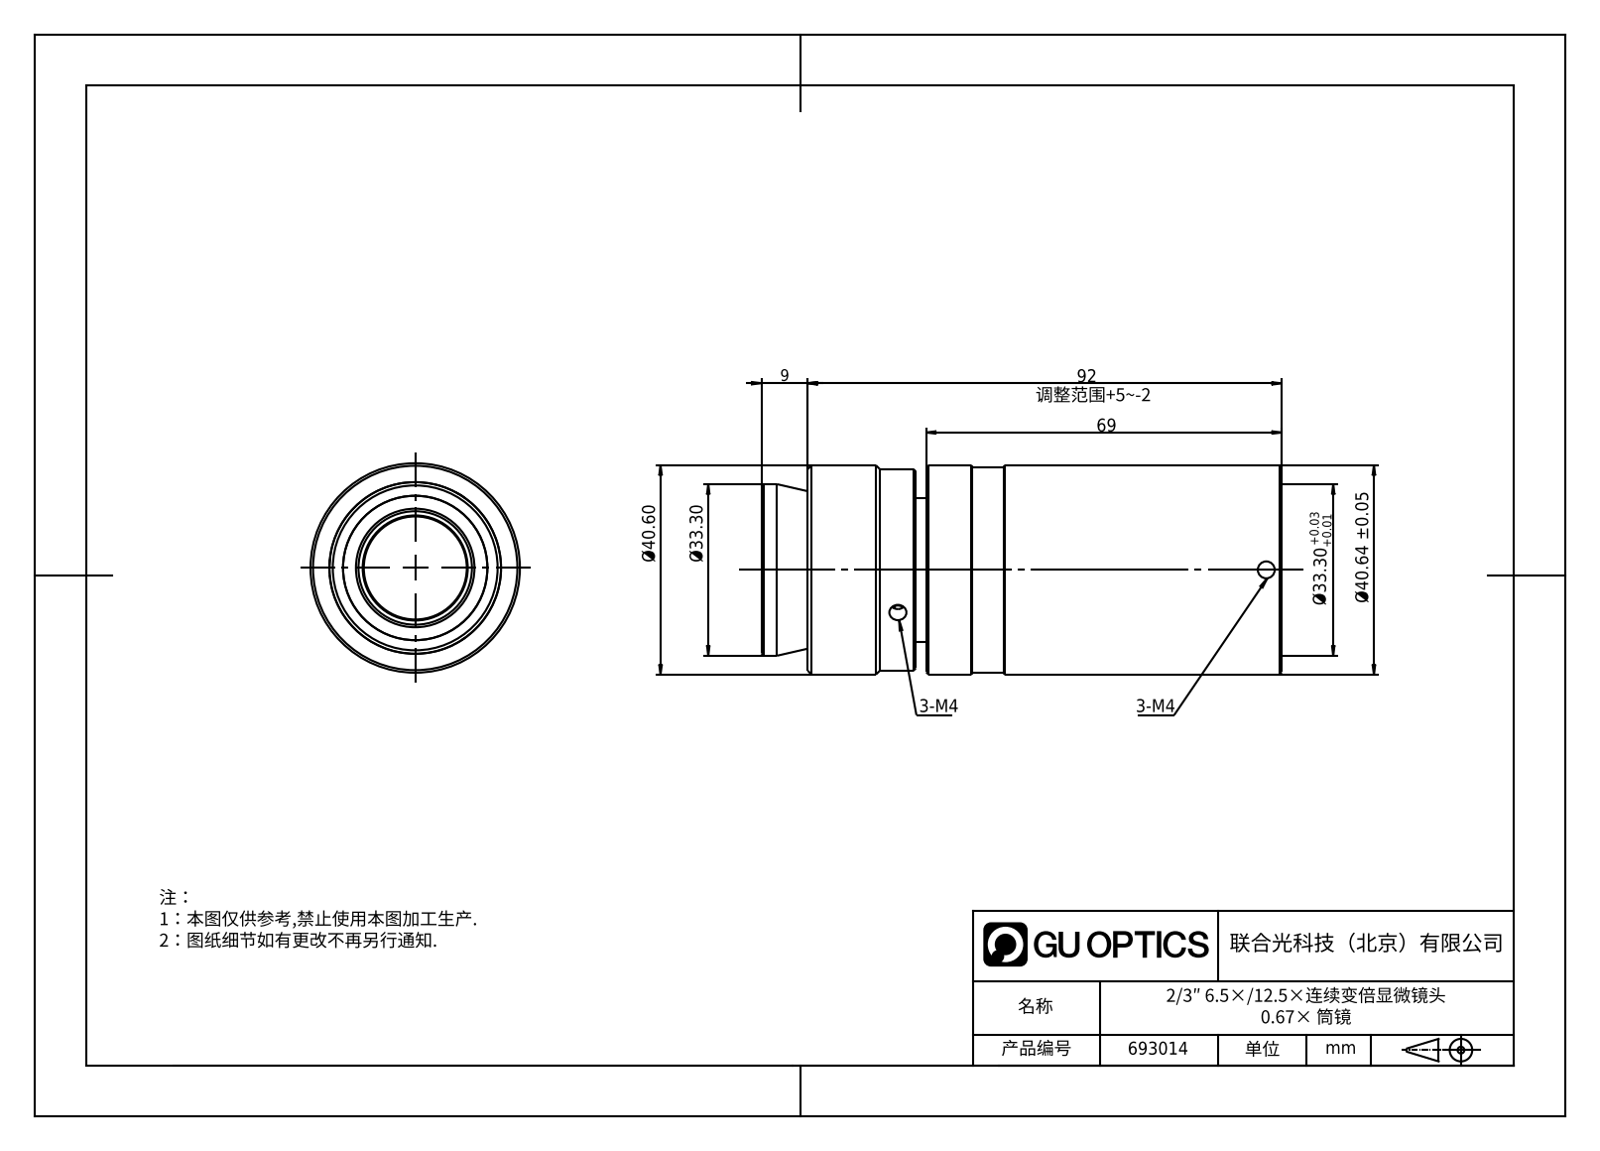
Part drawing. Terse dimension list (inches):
name: 693014
written by: SolidWorks 2020 (CONFIG_CONTROL_DESIGN)
unit: in
bodies: 2 solids, 47 faces (14 planar, 24 cylindrical, 9 other)
size: 3.976 × 1.6 × 1.6
volume: 3.632 in³; area: 45.63 in²
holes: 3× ⌀0.118, 3× ⌀0.13, 1× ⌀0.787, 1× ⌀0.906, 1× ⌀0.945, 1× ⌀1.081, 1× ⌀1.11, 1× ⌀1.181, 1× ⌀1.26, 1× ⌀1.311
bosses: 1× ⌀1.6, 1× ⌀1.575, 1× ⌀1.516, 1× ⌀1.102
face distances: 0.079, 0.709, 0.472, 0.906, 0.354, 2.795, 0.827, 1.181, 1.26, 0.787
